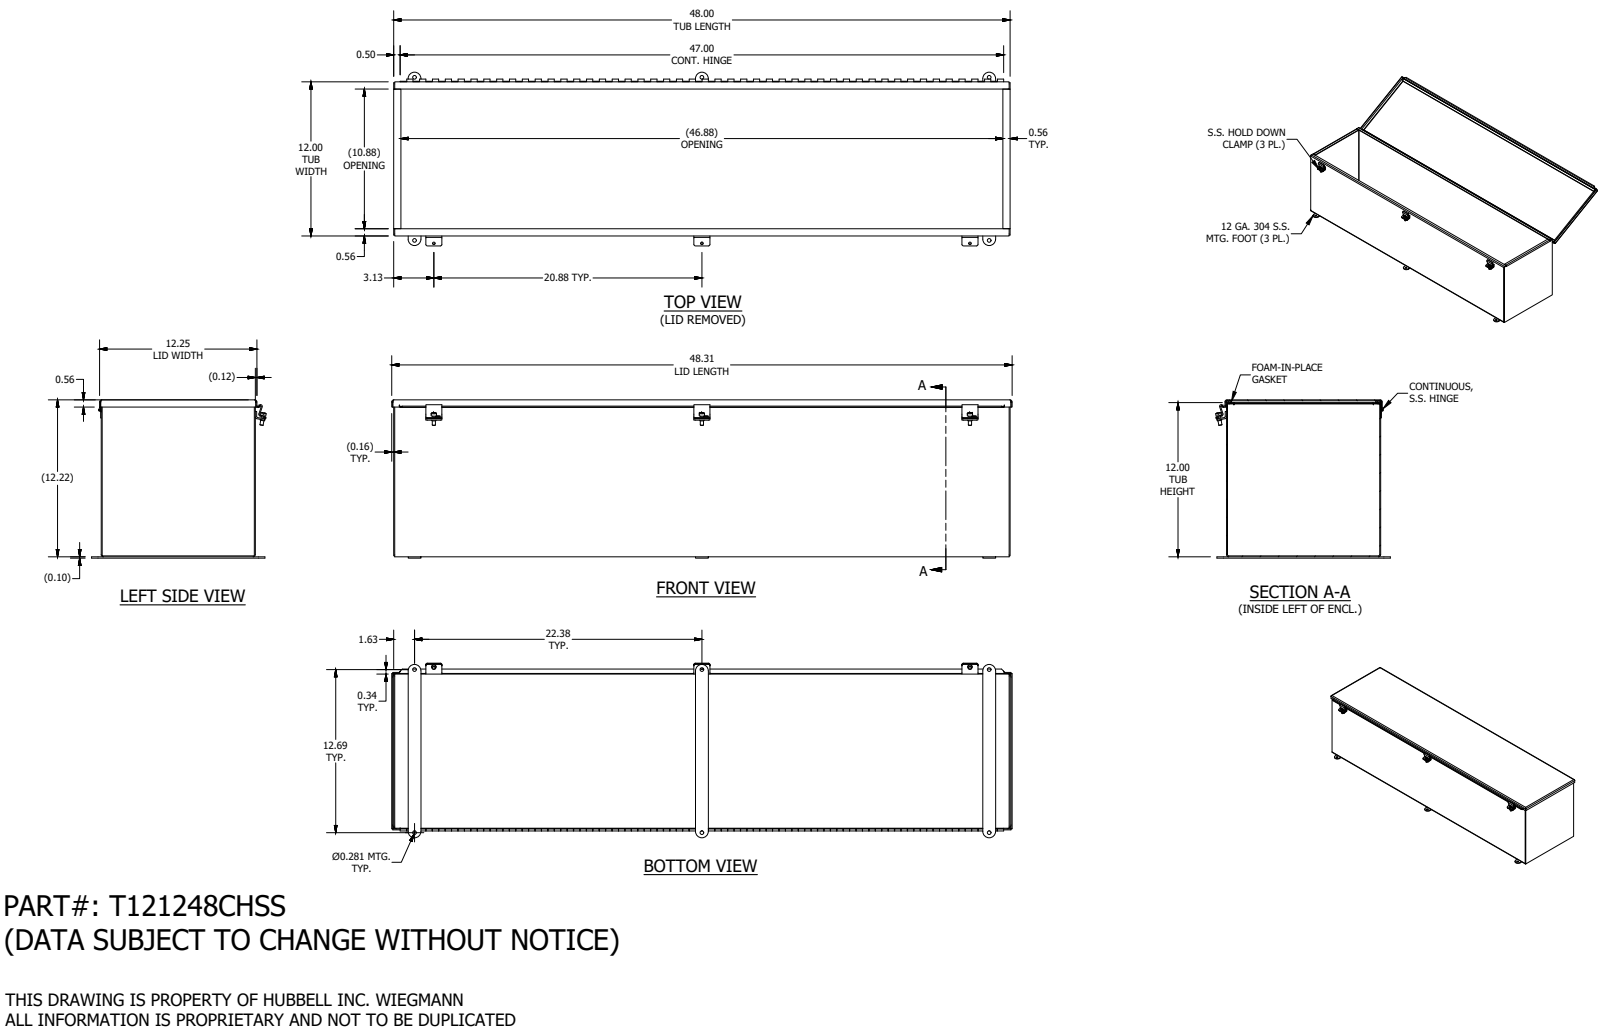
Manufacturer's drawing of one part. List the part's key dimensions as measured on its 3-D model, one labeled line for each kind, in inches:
Part name (STEP PRODUCT): T121248CHSS
STEP written by: SolidWorks 2019 (AUTOMOTIVE_DESIGN)
Units: inches
Bodies: 20 solids, 839 faces (503 planar, 297 cylindrical, 39 other)
Overall size (bounding box): 48.313 × 13.598 × 12.322
Volume: 218.7 in³ · Surface area: 5 852 in²
Round holes (diameter × count): ⌀0.11 ×6, ⌀0.281 ×6, ⌀0.196 ×3, ⌀0.116 ×1
Round bosses / shafts (diameter × count): ⌀0.41 ×3, ⌀0.344 ×3, ⌀0.25 ×3, ⌀0.2 ×1, ⌀0.1 ×1
Partial cylindrical surfaces — rounded edges, fillets, slot ends (radius × count): R0.125 ×12, R0.094 ×11, R0.168 ×11, R0.085 ×8, R0.133 ×6, R0.5 ×6, R0.242 ×4, R0.063 ×3
Main face-to-face distances: 0.074, 11.926, 12.144, 11.852, 12, 12.218, 12.07, 47.926, 47.852, 48
Hole centre spacings: 20.875, 22.375, 25.722, 0.75, 12.687, 20.875, 41.75, 44.75
